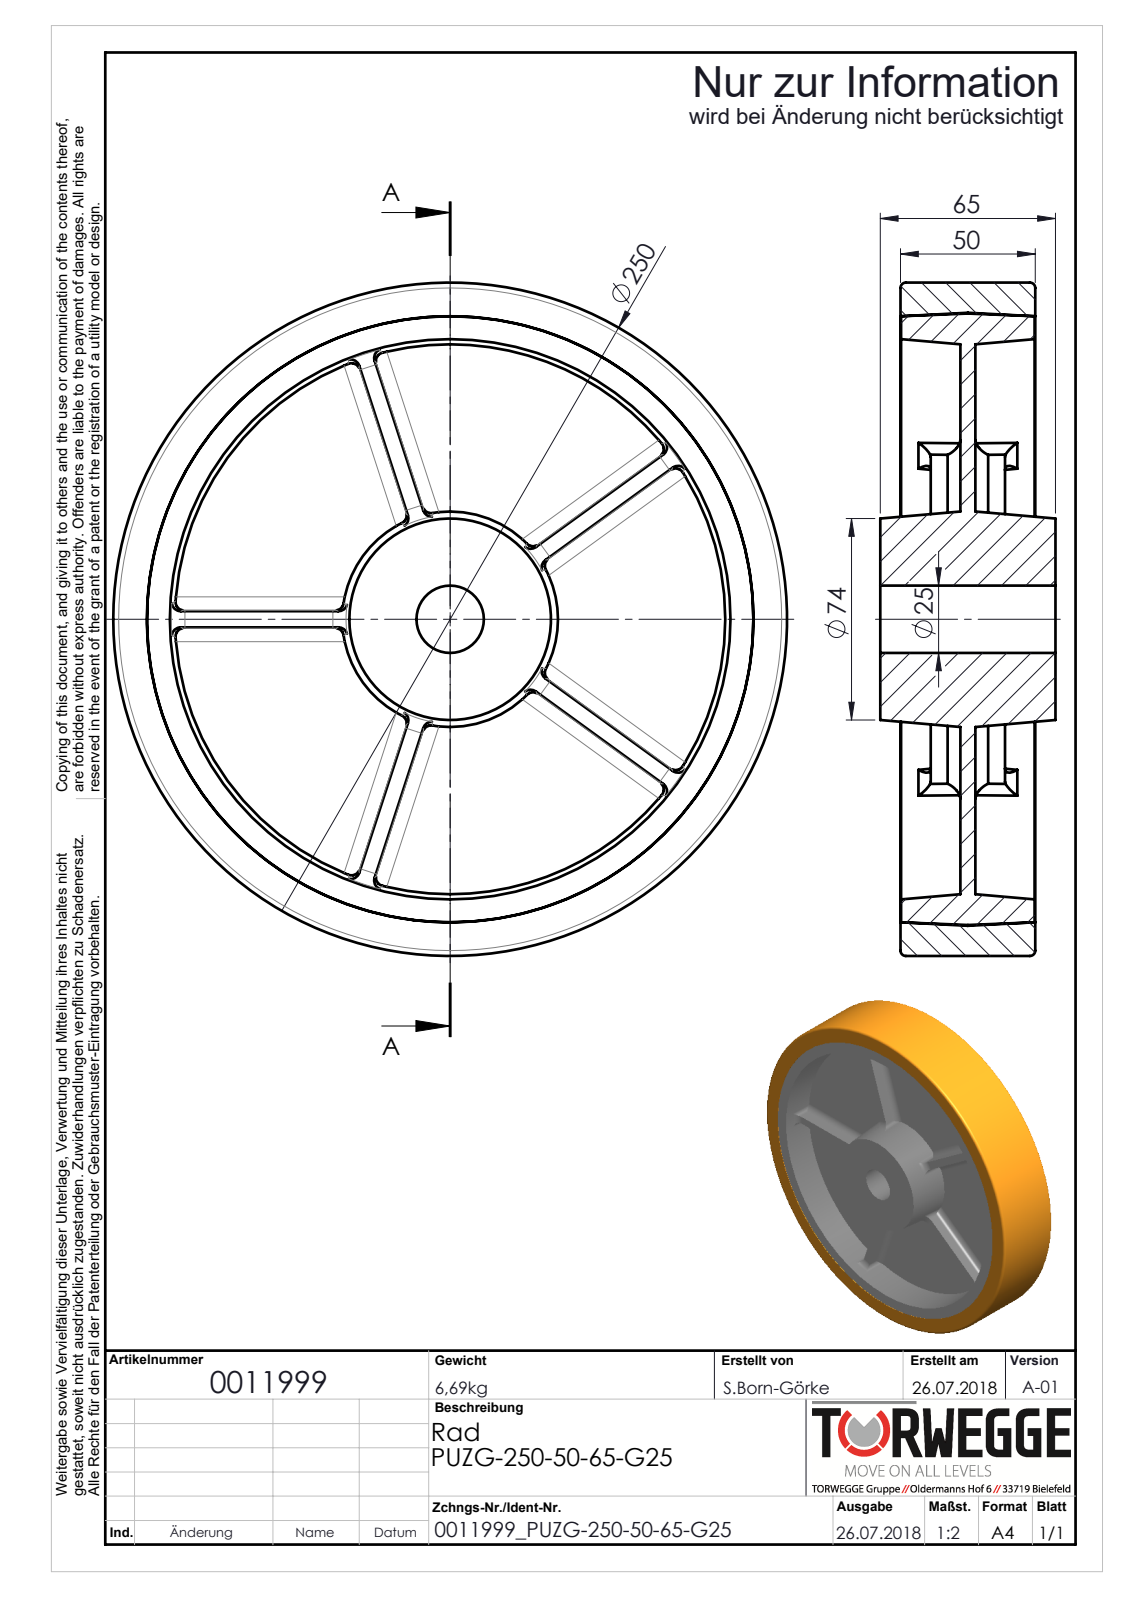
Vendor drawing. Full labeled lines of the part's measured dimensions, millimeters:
Part name (STEP PRODUCT): PUZG-250-50-65-G25_FELGE; PUZG-250-50-65-G25_Bandage; 0011999_PUZG-250-50-65-G25
STEP written by: SolidWorks 2018 (AUTOMOTIVE_DESIGN)
Units: millimetres
Bodies: 2 solids, 154 faces (46 planar, 24 cylindrical, 84 other)
Overall size (bounding box): 250 × 250 × 65
Volume: 1 274 000 mm³ · Surface area: 259 167 mm²
Round holes (diameter × count): ⌀25 ×1
Round bosses / shafts (diameter × count): ⌀250 ×1
Partial cylindrical surfaces — rounded edges, fillets, slot ends (radius × count): R5 ×20
Main face-to-face distances: 5.56, 22.22, 27.78, 27.56, 49.78, 22, 7.5, 7.72, 29.72, 35.28
